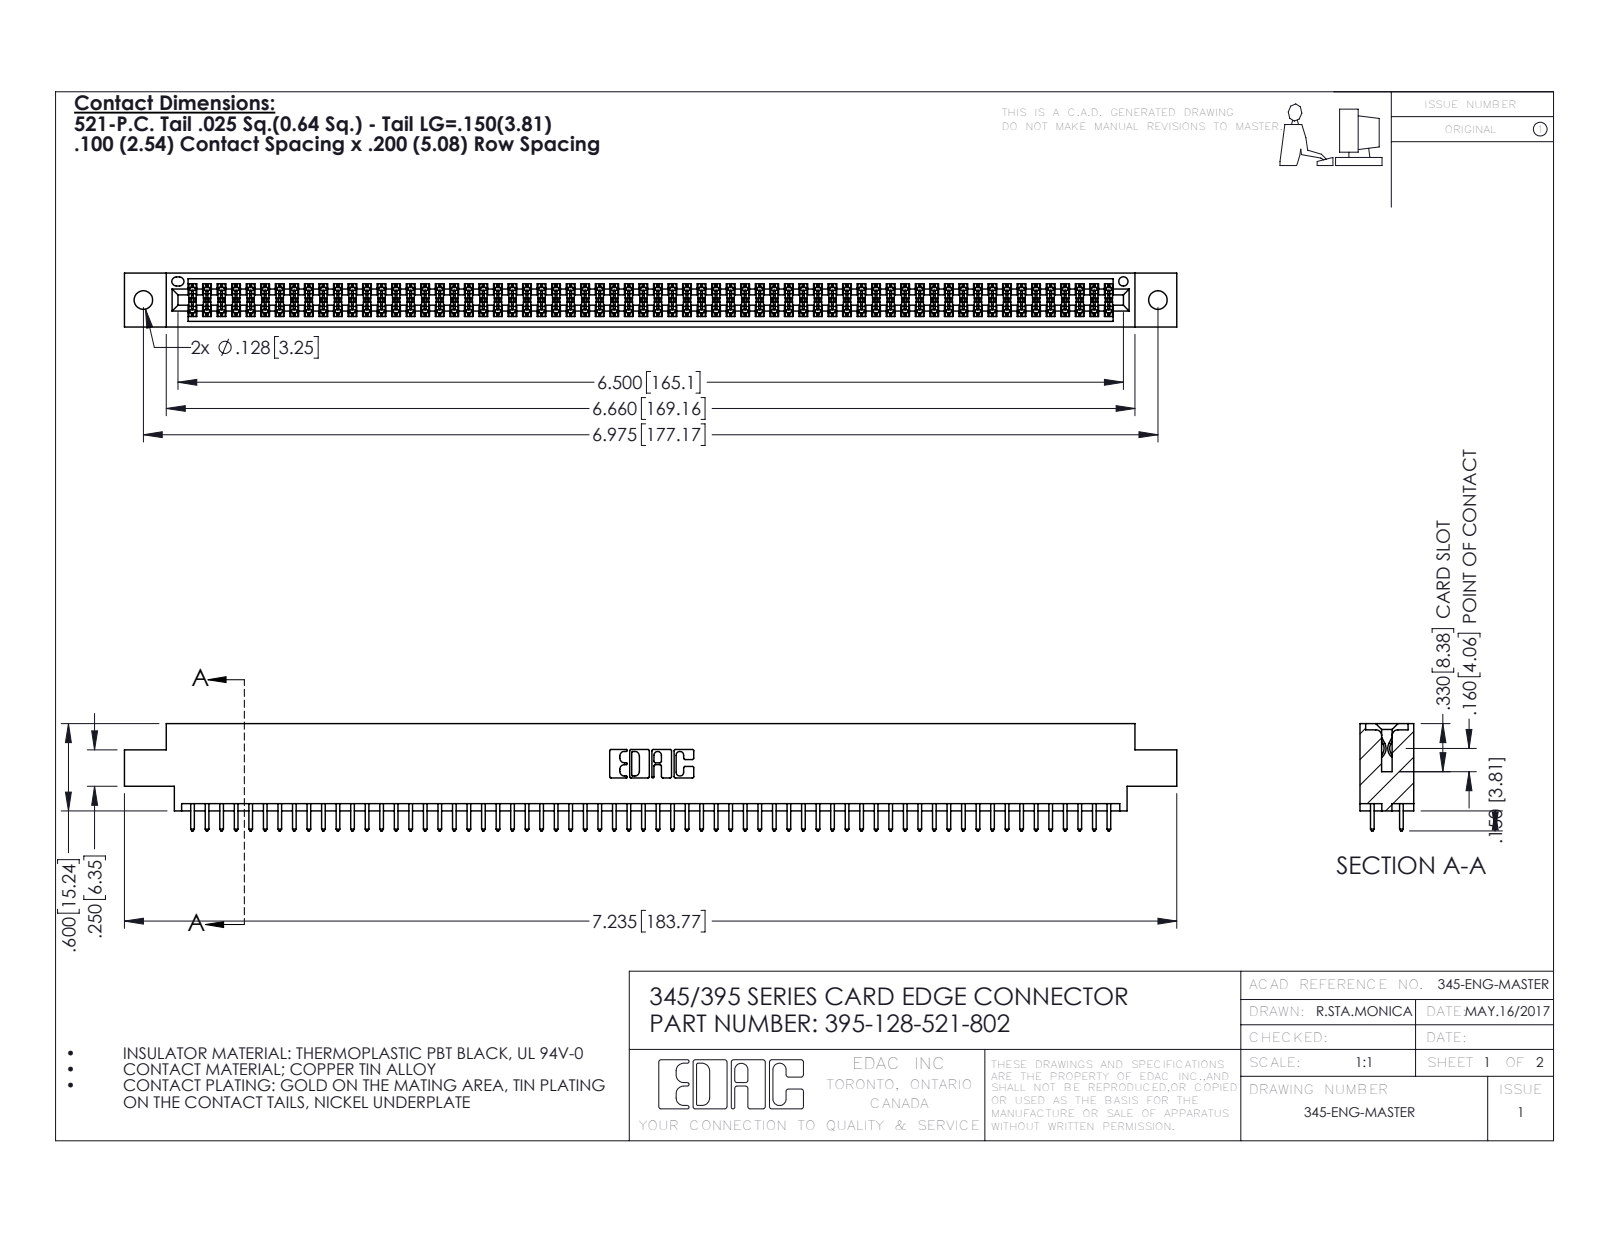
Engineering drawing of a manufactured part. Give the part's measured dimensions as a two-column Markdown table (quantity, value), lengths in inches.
| quantity | value |
| --- | --- |
| part name | 345-292-001_345-293-121; 345 Part_0.170 Offset - 0.128 Dia; 395-128-521-802 |
| STEP written by | SolidWorks 2016 (CONFIG_CONTROL_DESIGN) |
| units | inches |
| bodies | 129 solids, 6530 faces (4308 planar, 2222 cylindrical, 0 other) |
| overall size | 7.235 × 0.737 × 0.37 |
| volume | 1.089 in³ |
| surface area | 40.84 in² |
| round holes (diameter × count) | 0.128 × 2, 0.064 × 1 |
| partial cylindrical surfaces (radius × count) | 0.006 × 192, 0.01 × 128, 0.01 × 22, 0.007 × 6, 0.031 × 6, 0.026 × 3, 0.014 × 2, 0.019 × 2 |
| main face-to-face distances | 0.298, 0.072, 0.2, 0.37, 0.098, 0.272, 0.025, 0.225, 0.175, 0.149 |
| hole center spacings | 0.27, 6.739, 6.975 |
